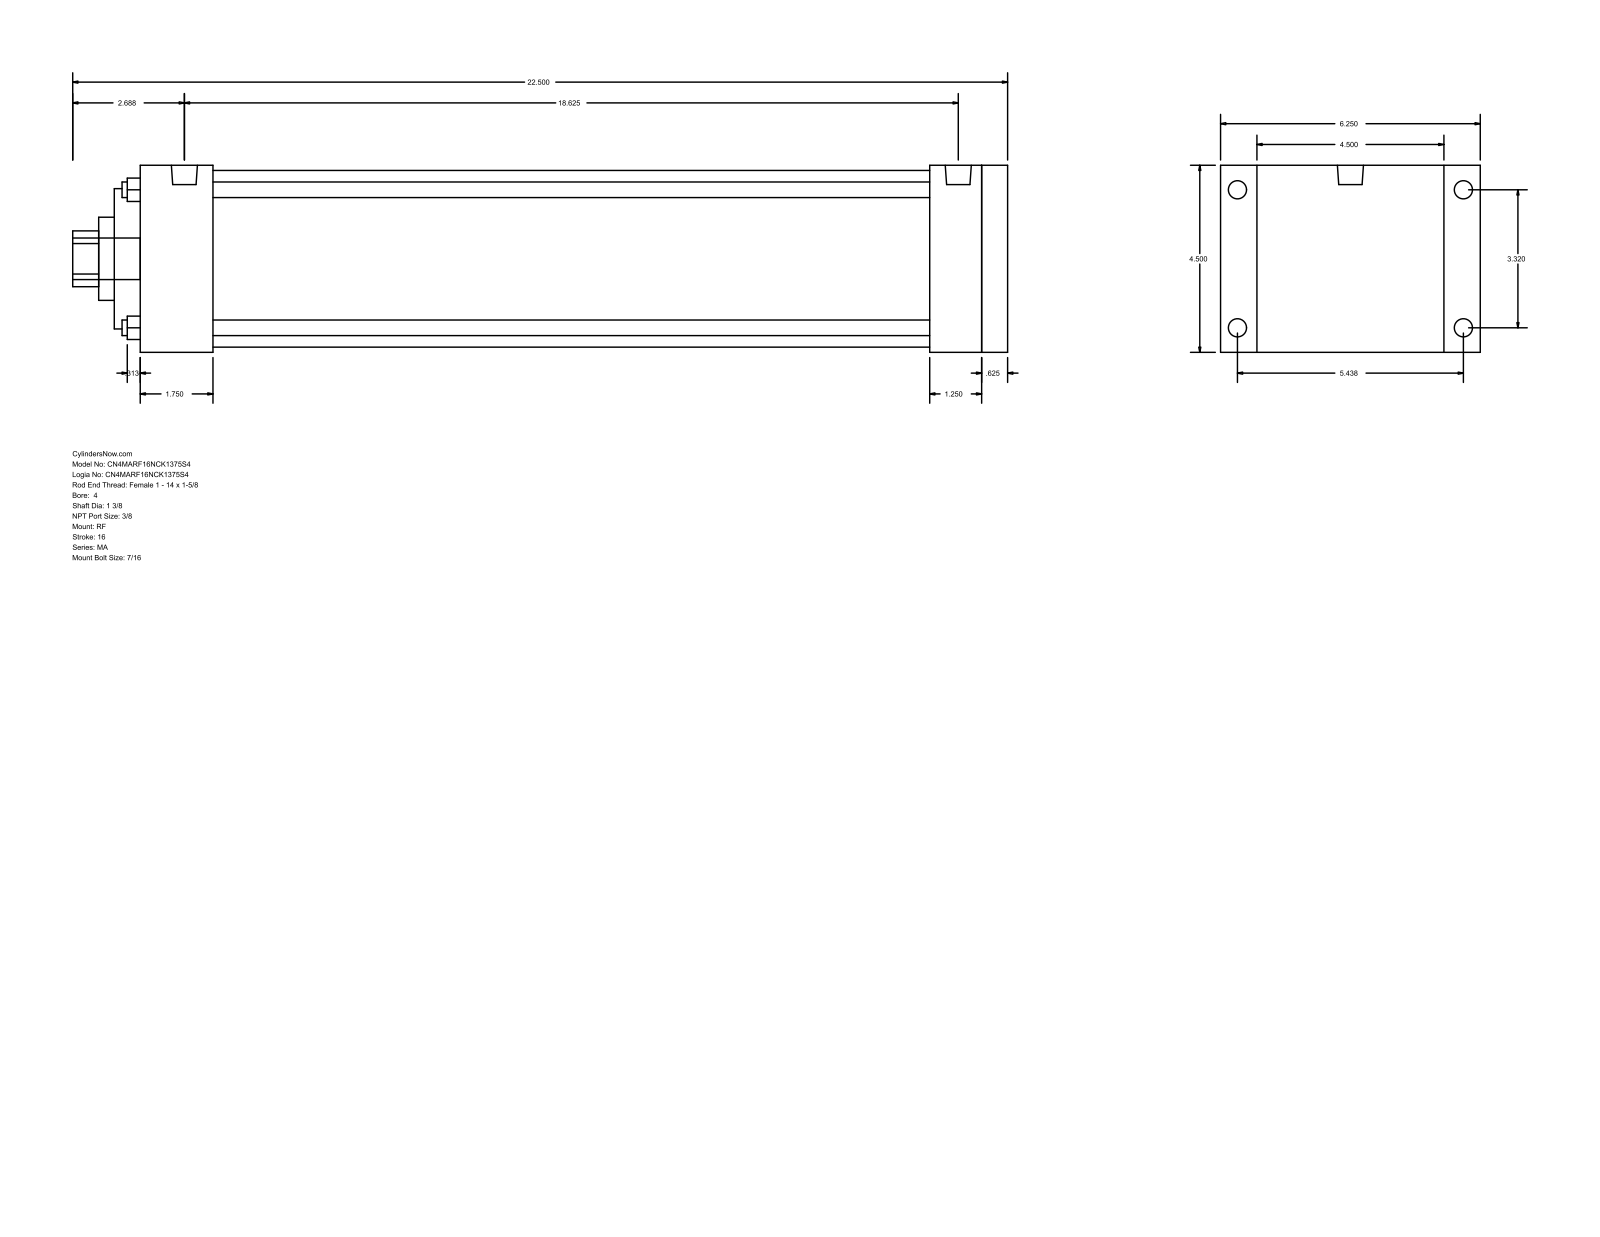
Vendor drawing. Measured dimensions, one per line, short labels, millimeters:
name: MA_RF__0400_1.375
written by: GSSL Pune (CONFIG_CONTROL_DESIGN)
unit: mm
bodies: 0 solids, 94 faces (65 planar, 29 cylindrical, 0 other)
size: 571.5 × 158.75 × 114.3
holes: 4× ⌀9.53, 1× ⌀34.92, 1× ⌀50.8, 1× ⌀85.72, 1× ⌀107.95
bosses: 8× ⌀11.11, 2× ⌀15.93, 1× ⌀25.4
rounds: 1× R17.06
face distances: 114.3, 530.23, 15.88, 514.35, 15.87, 530.22, 546.1, 22.23, 136.53, 498.48
hole spacings: 59.62, 84.32, 119.25
